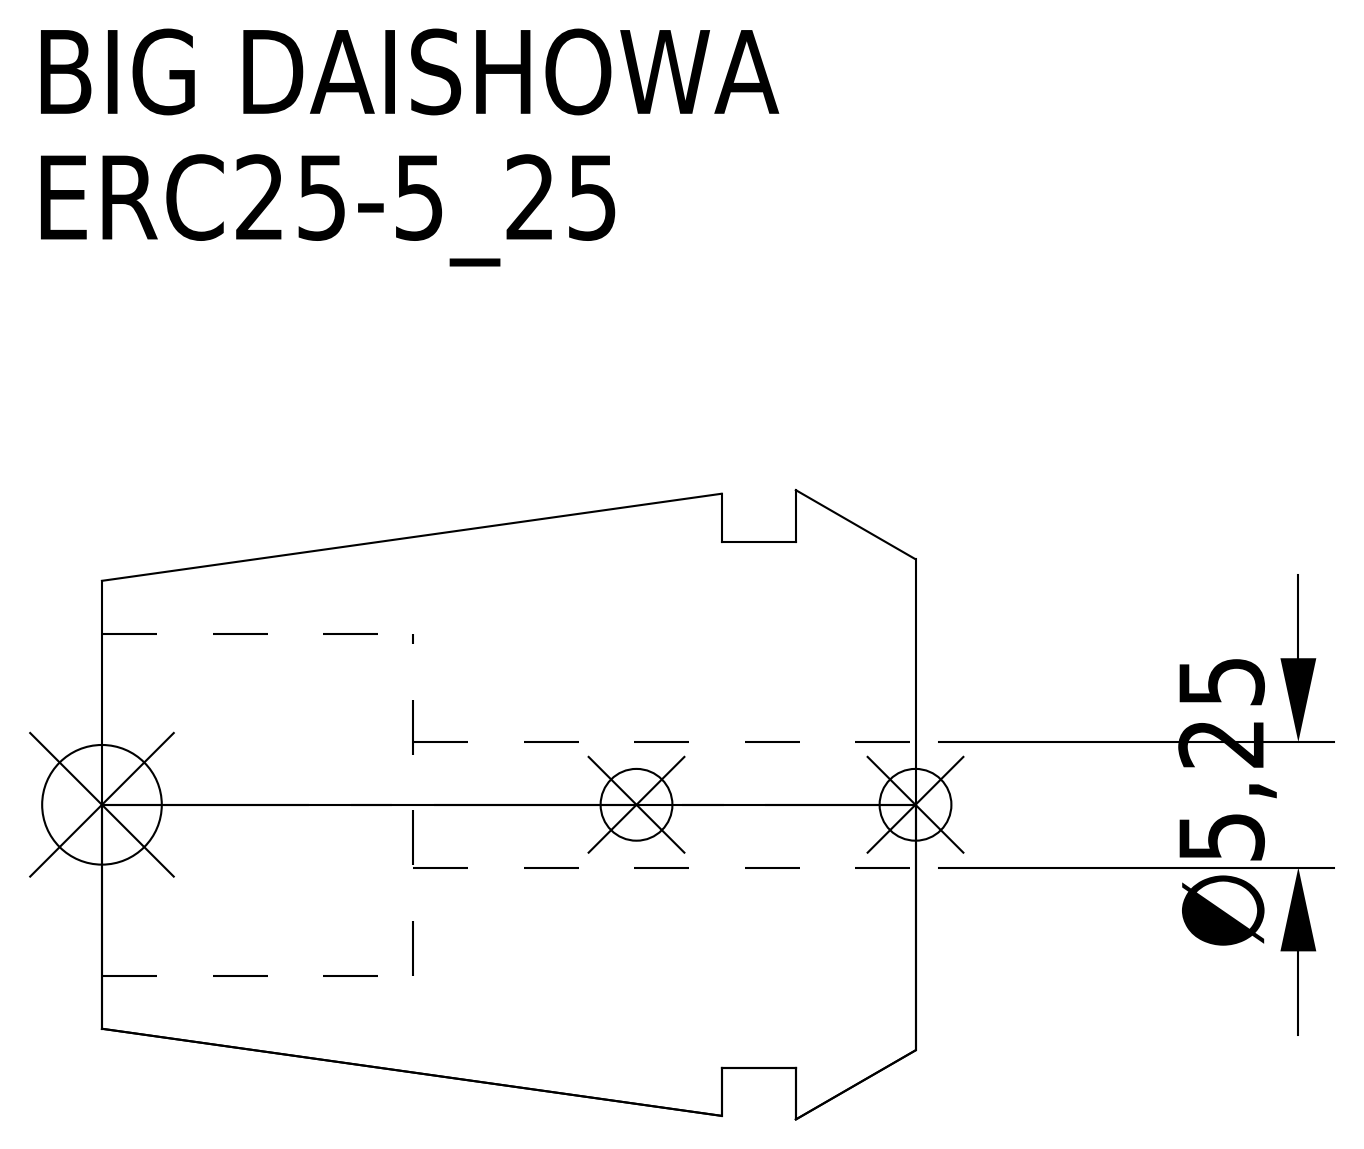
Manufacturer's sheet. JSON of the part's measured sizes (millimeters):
{"part_name": "ERC25-5_25", "step_written_by": "CREO PARAMETRIC BY PTC INC, 2016380 (AUTOMOTIVE_DESIGN)", "units": "millimeters", "bodies": {"solids": 1, "faces": 15, "planar": 5, "cylindrical": 6, "other": 4}, "overall_size": [34, 26.3, 26.3], "volume_mm3": 11060, "surface_area_mm2": 4283, "round_holes": [[5.25, 1], [14.3, 1]], "round_bosses_or_shafts": [[22, 1]], "face_to_face_distances": [5, 8.1, 3.1, 21, 16, 12.9, 34, 29, 25.9, 13]}
